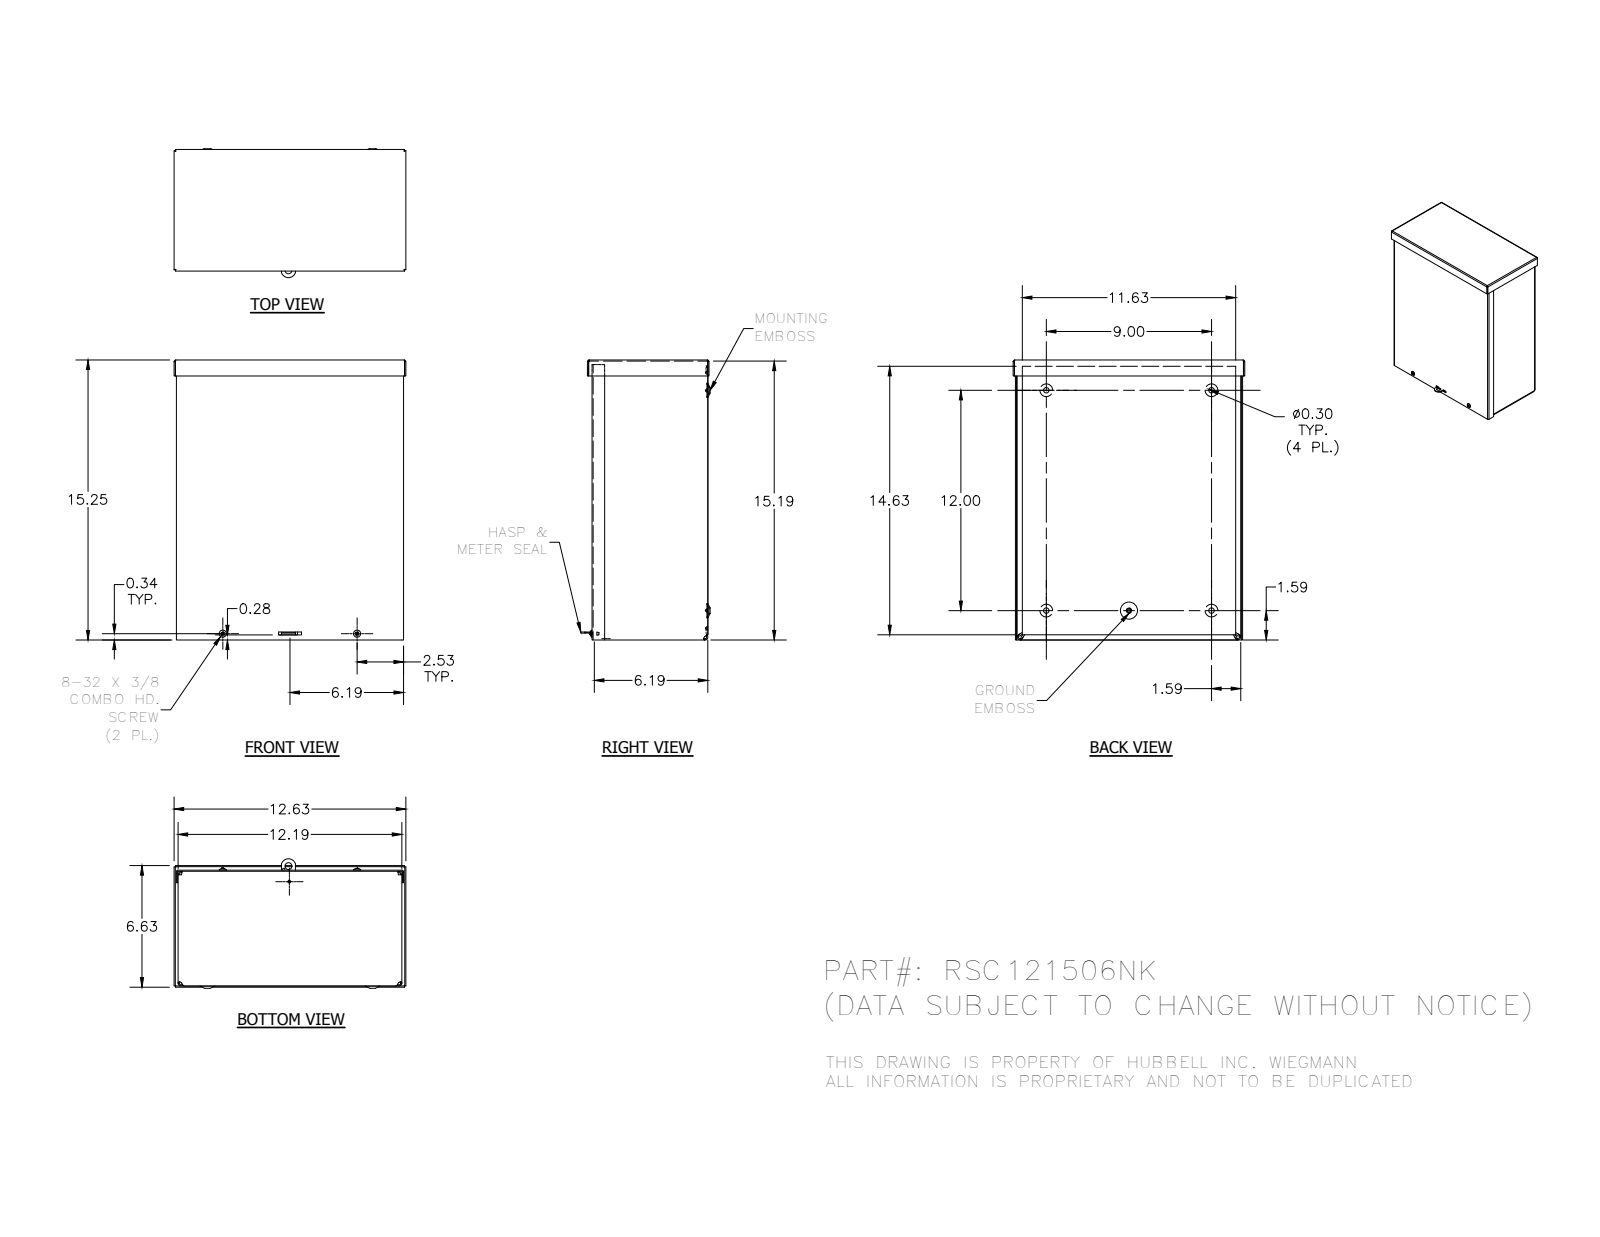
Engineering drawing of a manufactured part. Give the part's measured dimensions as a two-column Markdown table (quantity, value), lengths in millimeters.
| quantity | value |
| --- | --- |
| part name | RSC121506NK_WRAP; RSC1215NK_LID; RSC1206NK_CAP; 3183 (+3 more) |
| STEP written by | Autodesk Inventor 2014 (AUTOMOTIVE_DESIGN) |
| units | millimeters |
| bodies | 7 solids, 377 faces (163 planar, 78 cylindrical, 136 other) |
| overall size | 387.36 × 320.68 × 180.97 |
| volume | 916 197 mm³ |
| surface area | 1 175 000 mm² |
| round holes (diameter × count) | 7.62 × 4, 7.95 × 4, 3.76 × 2, 3.17 × 1, 3.45 × 1, 3.96 × 1, 4.19 × 1, 9.52 × 1 |
| round bosses / shafts (diameter × count) | 9.75 × 2, 4.17 × 2, 5.8 × 1 |
| partial cylindrical surfaces (radius × count) | 0.79 × 8, 2.37 × 8, 3.17 × 8, 4.75 × 8, 1.4 × 4, 1.57 × 4, 2.38 × 4, 2.97 × 4 |
| main face-to-face distances | 1.58, 1.57, 158.73, 157.15, 307.99, 1.59, 160.32, 158.74, 384.19, 3.15 |
| hole center spacings | 34.43, 114.3, 185.75, 228.6, 304.8, 325.52, 332.44, 337.26 |
